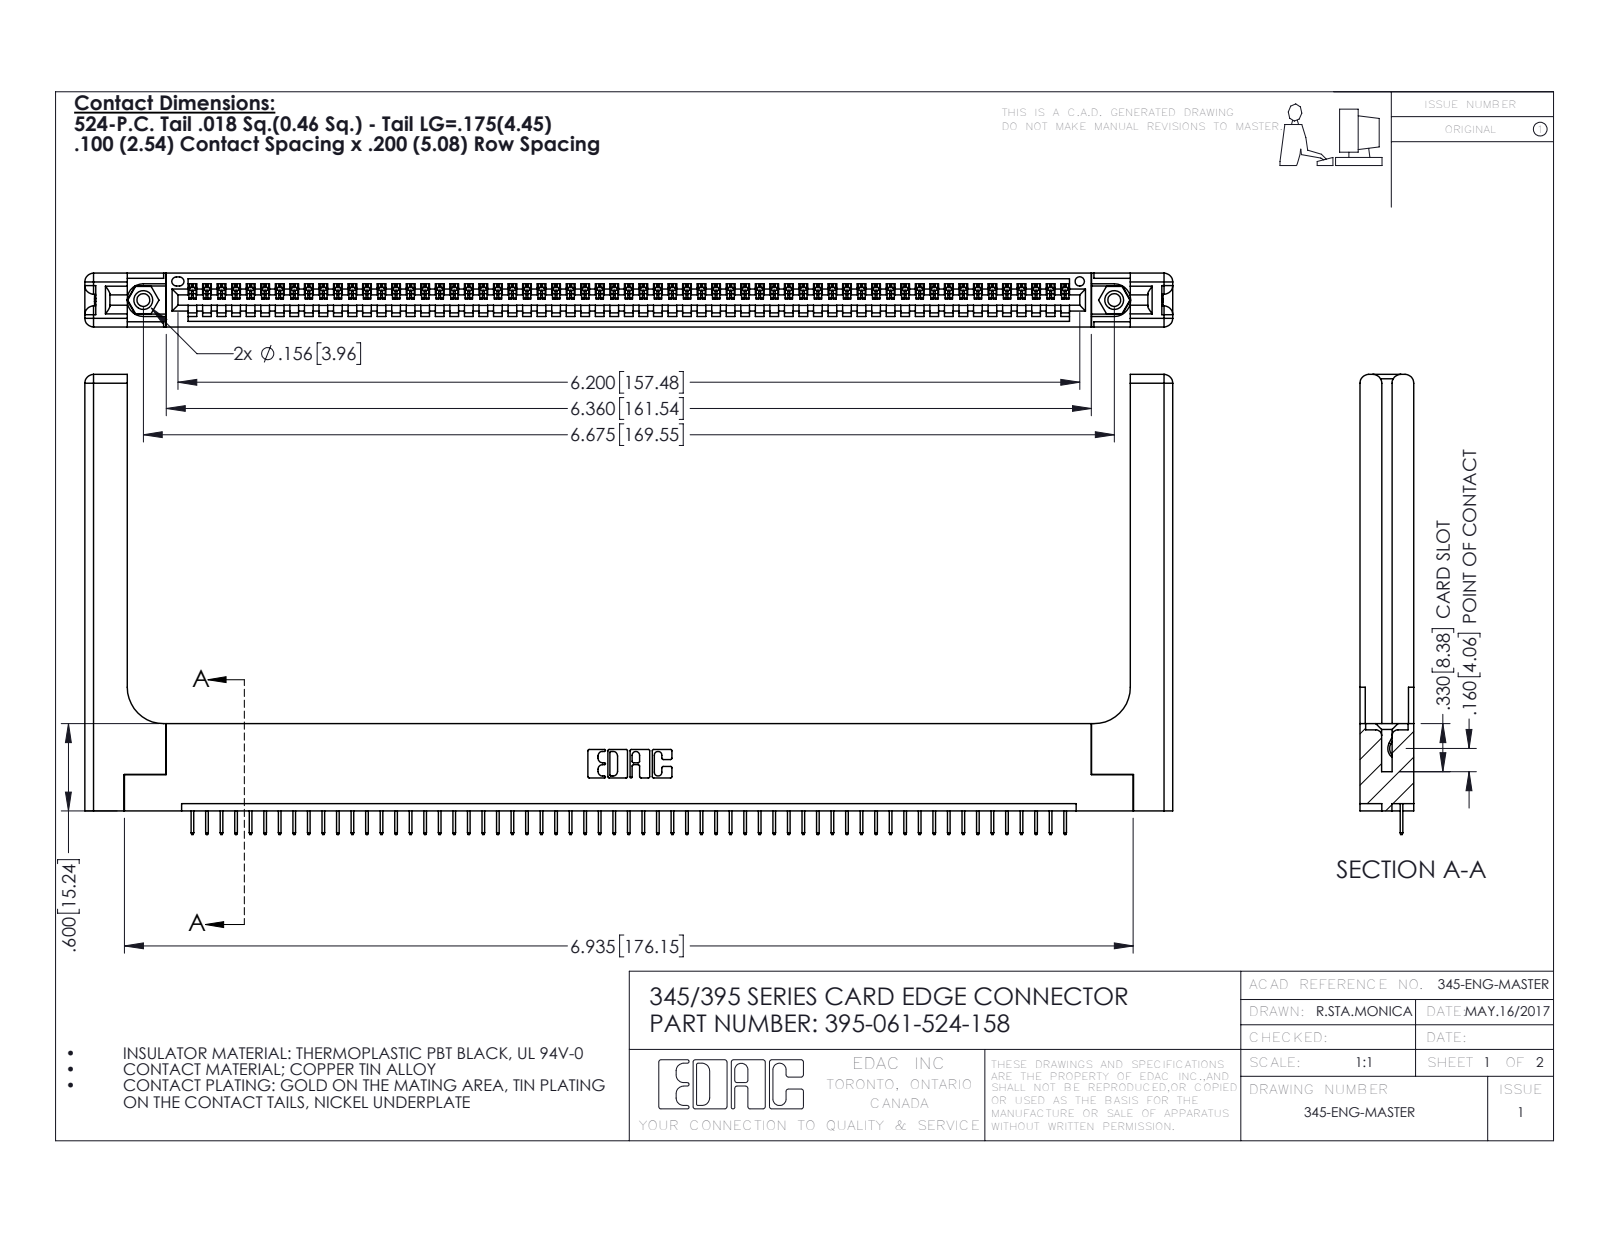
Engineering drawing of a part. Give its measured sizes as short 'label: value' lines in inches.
name: 345 Part_Flush Mounting Lugs - 0.156 Dia-TH; 345-220-058_345-220-058; 395-061-524-158; 345-292-001_345-293-124 (+1 more)
written by: SolidWorks 2016 (CONFIG_CONTROL_DESIGN)
unit: in
bodies: 66 solids, 4164 faces (3034 planar, 1070 cylindrical, 60 other)
size: 7.479 × 3.162 × 0.37
volume: 1.615 in³; area: 44.42 in²
holes: 2× ⌀0.089, 2× ⌀0.125, 2× ⌀0.156, 1× ⌀0.064
bosses: 2× ⌀0.155
rounds: 122× R0.006, 22× R0.01, 16× R0.06, 6× R0.007, 6× R0.031, 3× R0.026, 2× R0.03, 2× R0.031
face distances: 0.072, 0.37, 0.298, 0.2, 0.098, 0.272, 0.025, 0.225, 0.148, 0.15
hole spacings: 0.27, 6.439, 6.675
